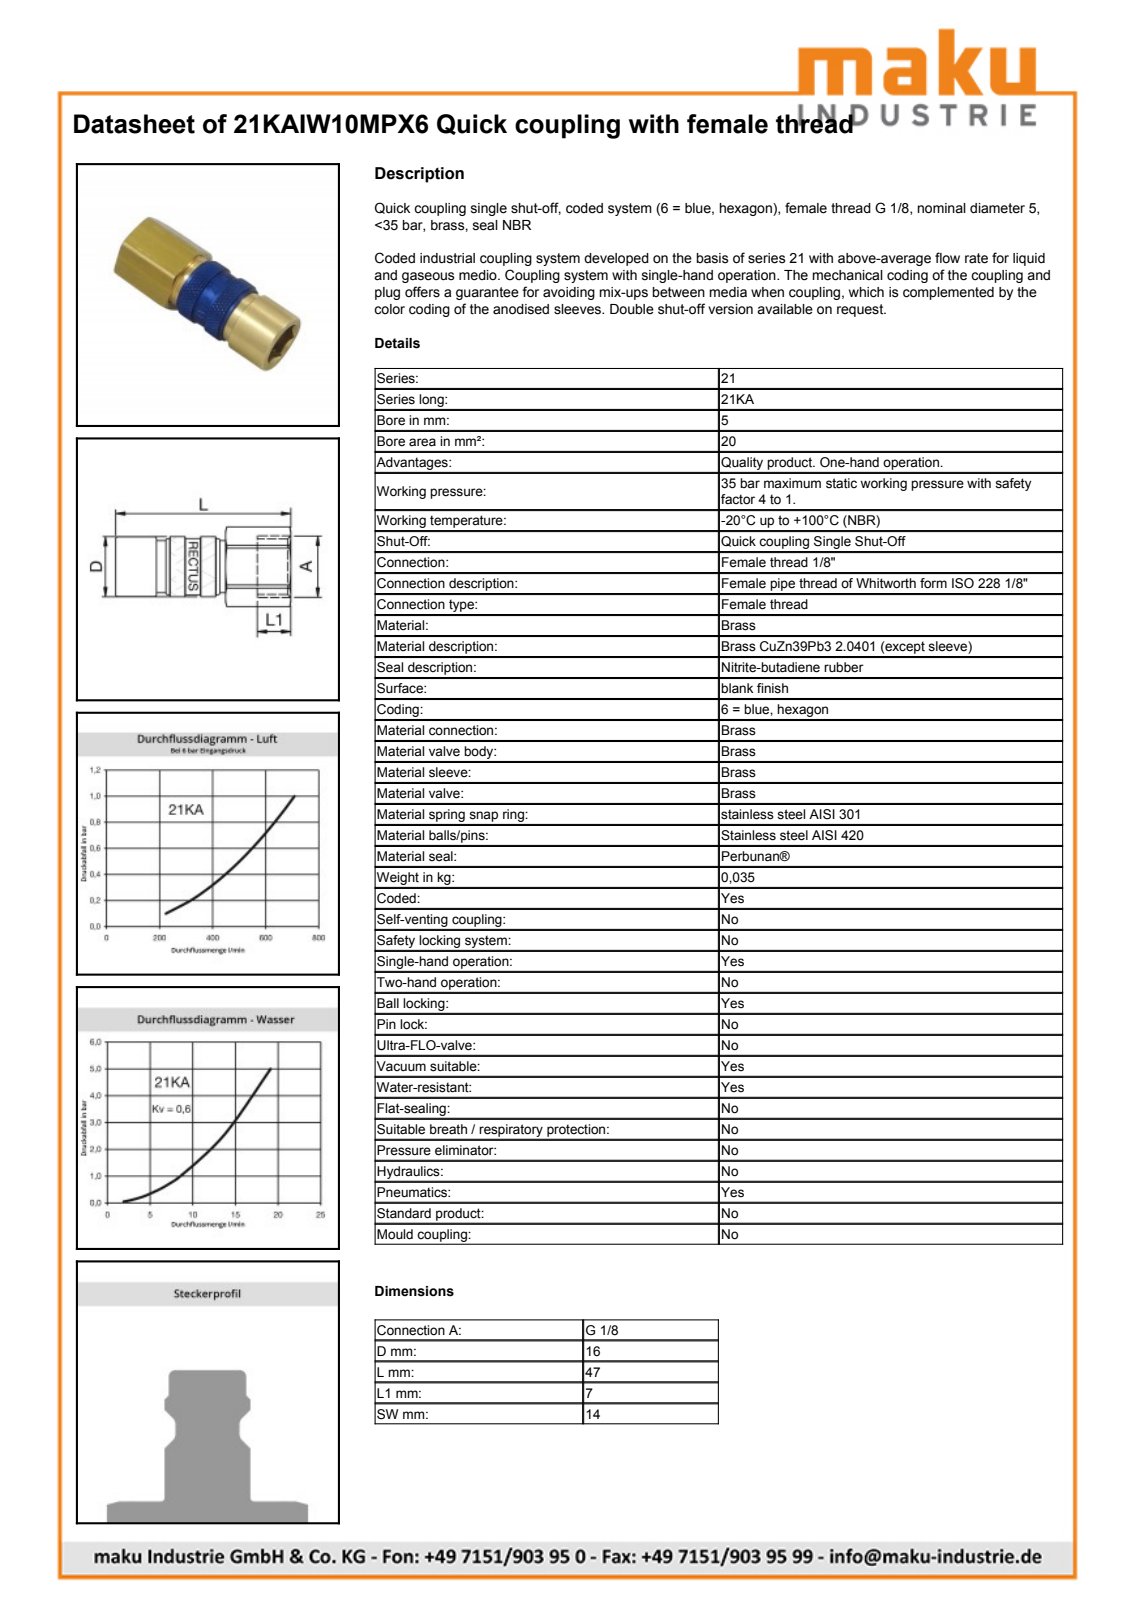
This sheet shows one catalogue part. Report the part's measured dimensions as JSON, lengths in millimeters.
{"part_name": "D110099", "step_written_by": "Autodesk Inventor 2013 (AUTOMOTIVE_DESIGN)", "units": "millimeters", "bodies": {"solids": 1, "faces": 460, "planar": 152, "cylindrical": 64, "other": 244}, "overall_size": [45, 16.15, 16.15], "volume_mm3": 6444, "surface_area_mm2": 4462, "round_holes": [[8.57, 1], [11.46, 1], [12.1, 1], [12.15, 1], [14, 1]], "round_bosses_or_shafts": [[16.15, 1], [15.8, 1], [15.1, 1], [12, 1], [11.4, 1], [11.28, 1]], "partial_cylinders_radius": [[7.45, 1]], "face_to_face_distances": [14, 10, 35, 45, 36.52, 26.52, 8.48, 15, 20, 25]}
